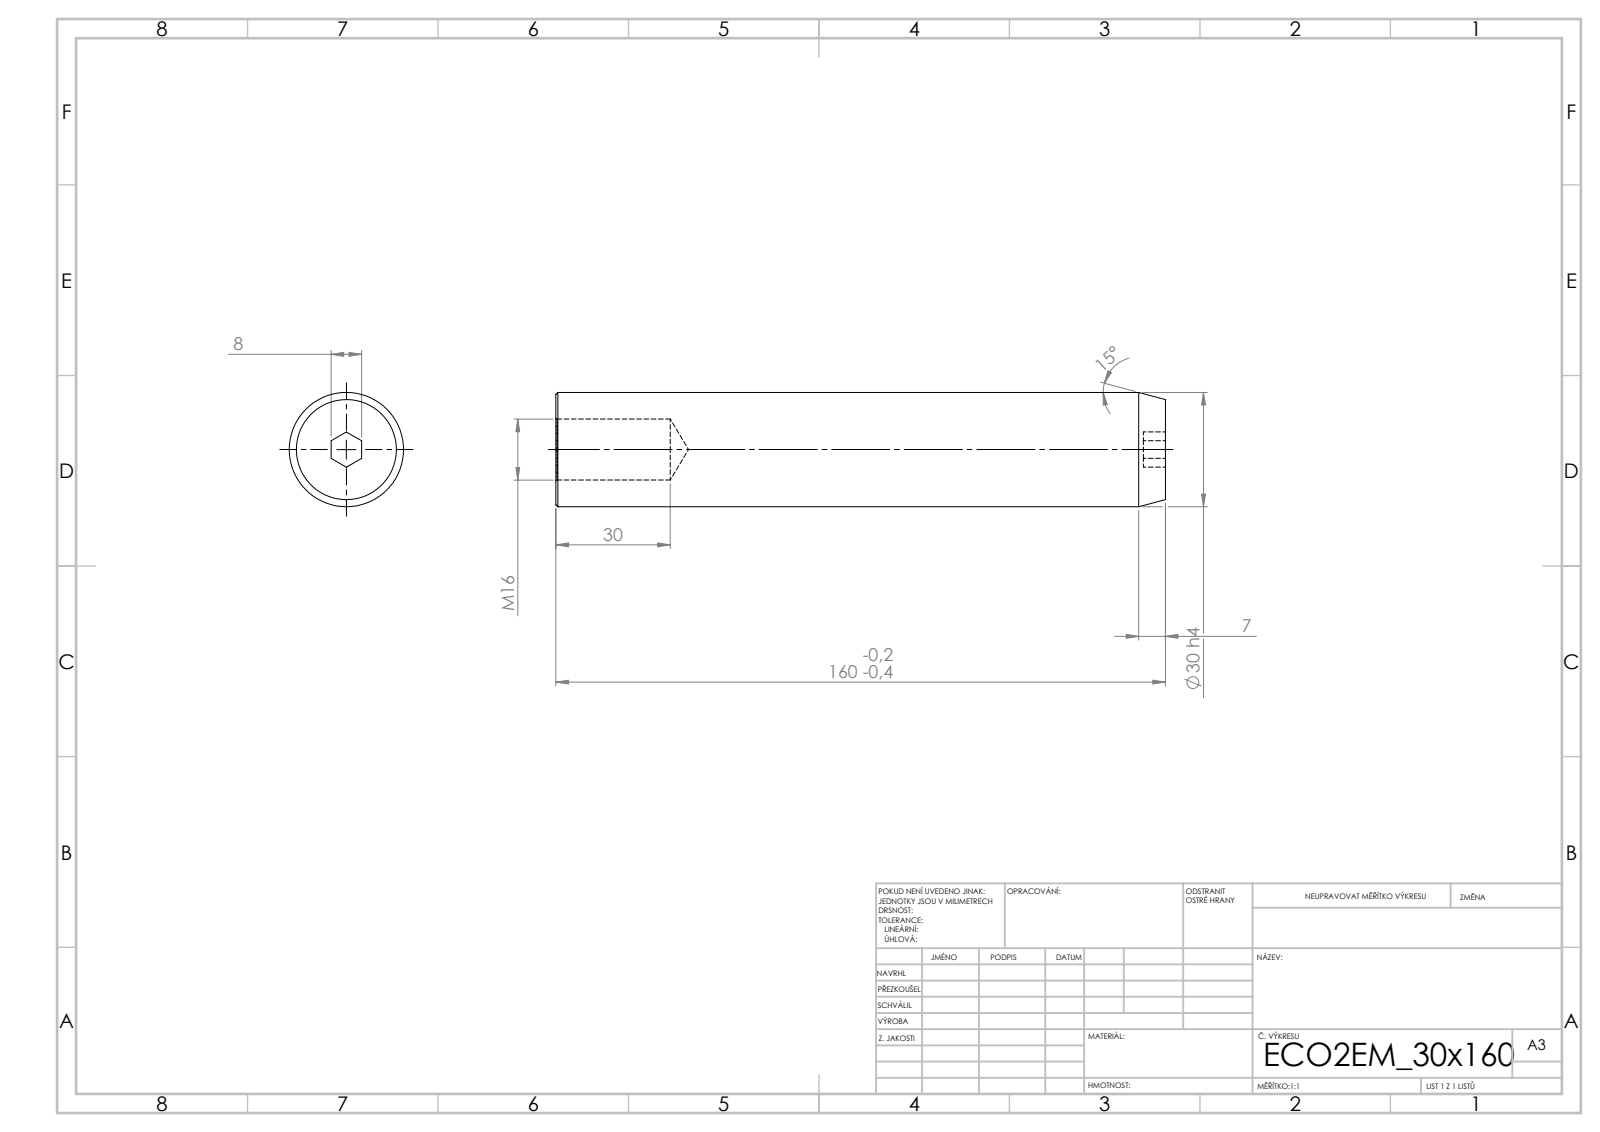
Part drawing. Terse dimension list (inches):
written by: SolidWorks 2019 (CONFIG_CONTROL_DESIGN)
unit: in
bodies: 1 solid, 21 faces (9 planar, 4 cylindrical, 8 other)
size: 6.299 × 1.181 × 1.181
volume: 6.457 in³; area: 27.86 in²
holes: 1× ⌀0.63
bosses: 1× ⌀1.181
face distances: 6.299, 0.315, 0.228, 6.071
